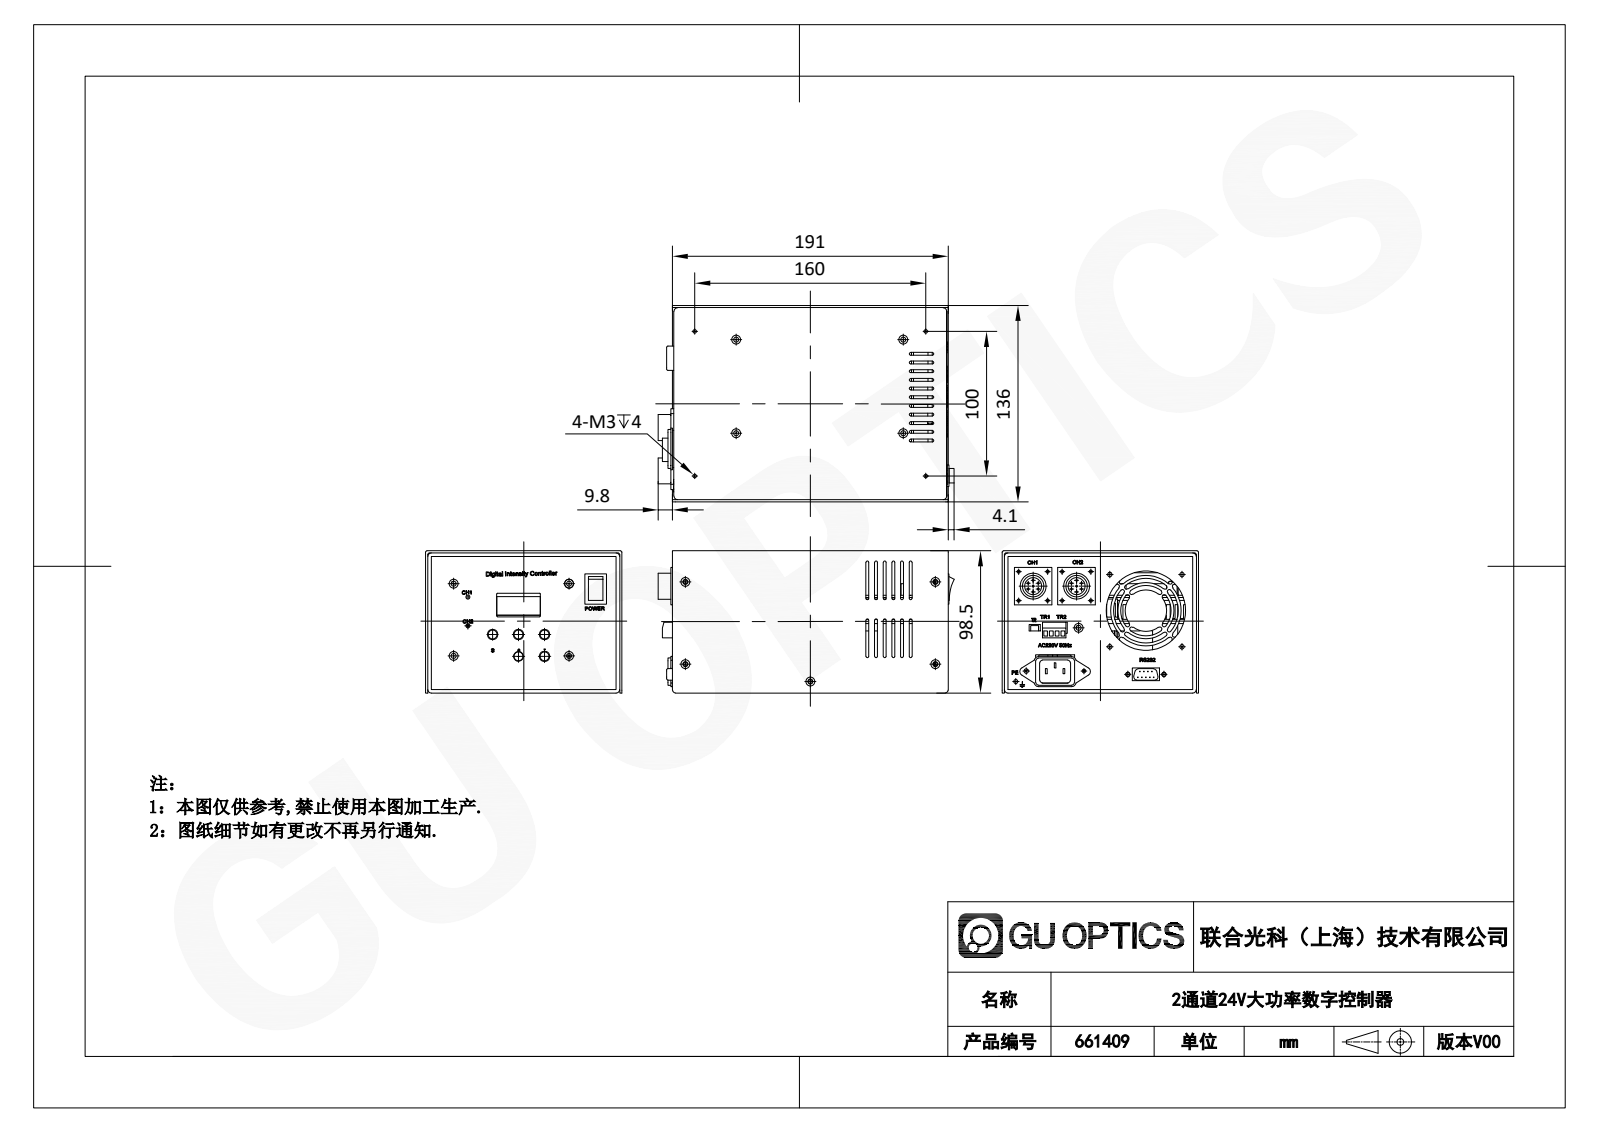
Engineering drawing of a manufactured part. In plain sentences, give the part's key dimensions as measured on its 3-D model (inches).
The part is named "661409". Its 3-D file was written by "SolidWorks 2020 (CONFIG_CONTROL_DESIGN)". It is 18 solids with 2336 faces: 1245 planar, 597 cylindrical and 494 other. Overall it measures 8.067 by 5.354 by 3.878 inches. Its volume is 26.22 cubic inches and its surface area 713.7 square inches. Round holes: 23 of diameter 0.138, 15 of diameter 0.134, 14 of diameter 0.059, 13 of diameter 0.098, 11 of diameter 0.118, 10 of diameter 0.091, 9 of diameter 0.03, 7 of diameter 0.126, 5 of diameter 0.335, 4 of diameter 0.248, 4 of diameter 0.283, 2 of diameter 0.098. Round bosses or shafts: 9 of diameter 0.039, 5 of diameter 0.252, 2 of diameter 0.709, 2 of diameter 0.472, 1 of diameter 1.929, 1 of diameter 1.535, 1 of diameter 1.142, 1 of diameter 0.95. Partial cylindrical surfaces (rounded edges, fillets, slot ends): 74 of radius 0.039, 32 of radius 0.079, 12 of radius 0.02, 12 of radius 0.098, 8 of radius 0.059, 8 of radius 0.059, 8 of radius 0.059, 6 of radius 0.118. The main face-to-face distances are 0.059, 3.819, 0.063, 5.295, 5.236, 3.76, 3.878, 0.118, 7.382, 7.441. The hole center spacings are 0.787, 1.969, 0.557, 0.88, 1.181, 0.431, 1.113, 1.392.
